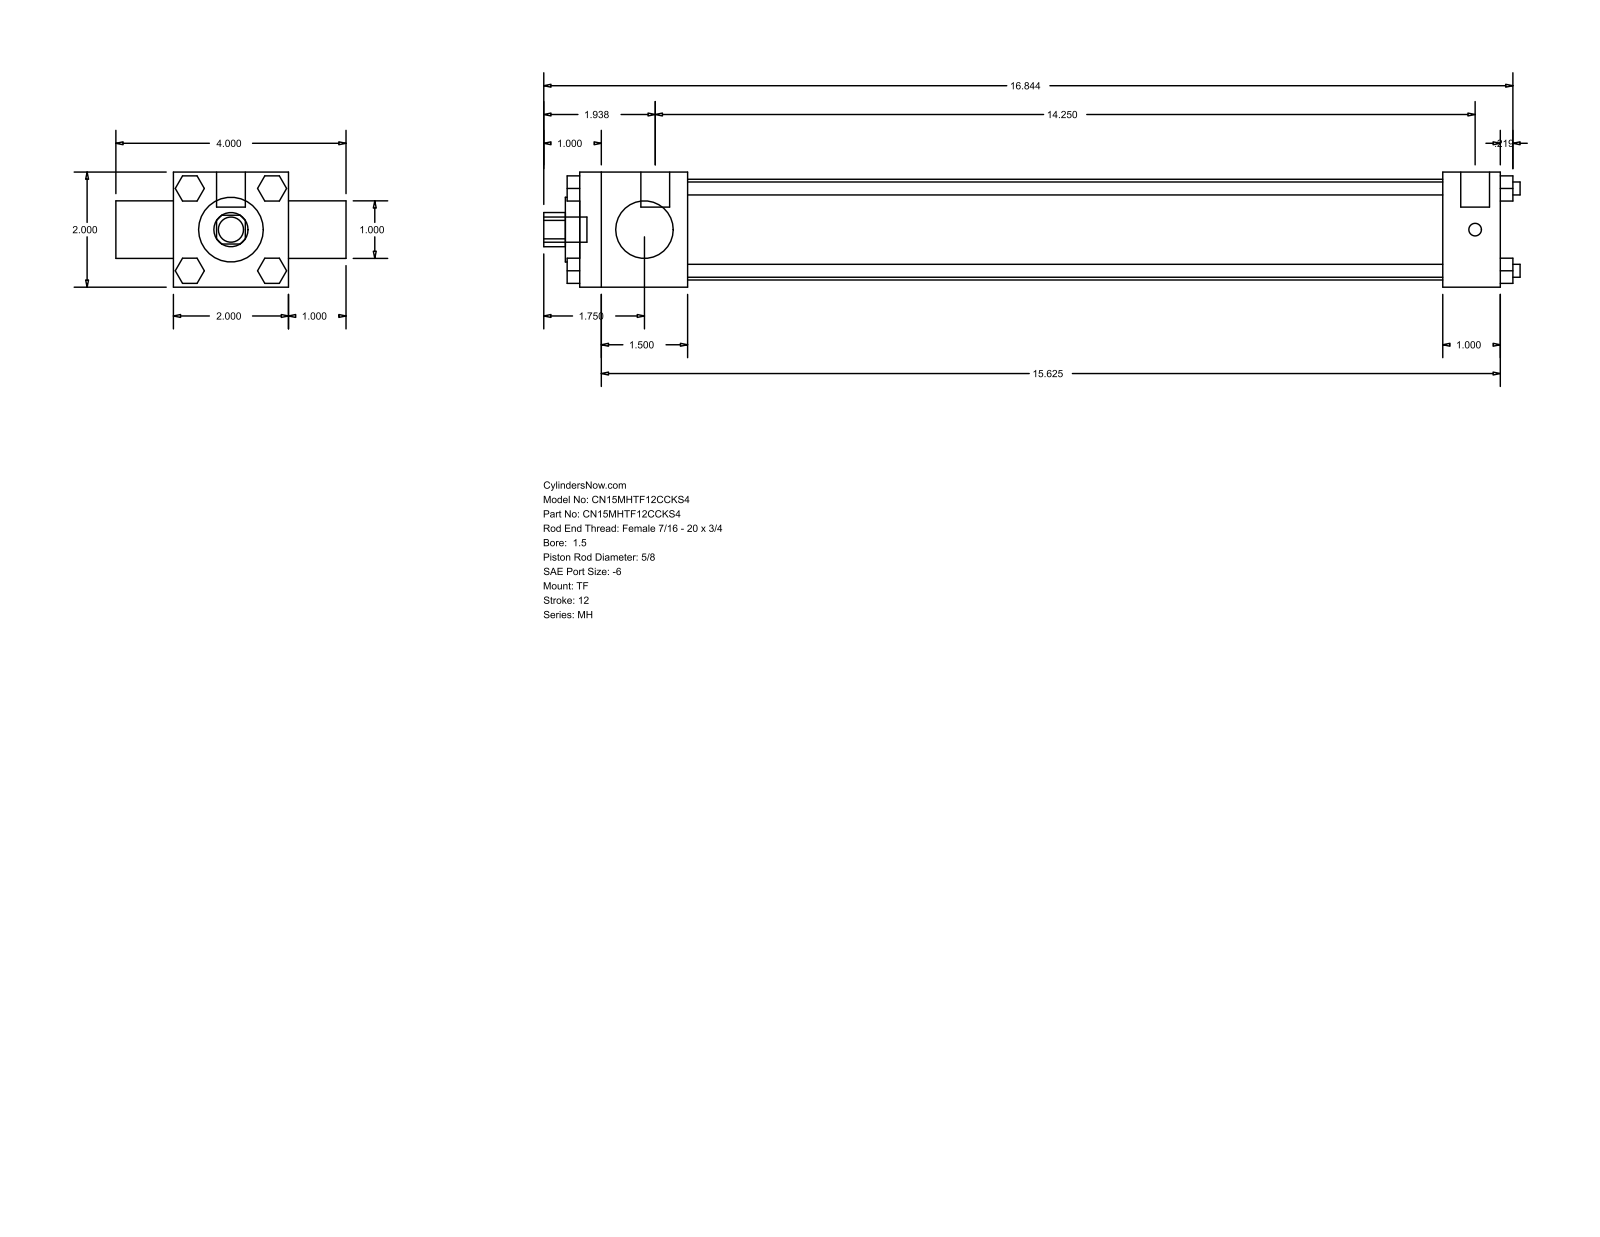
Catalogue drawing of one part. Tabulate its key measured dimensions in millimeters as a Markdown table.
| quantity | value |
| --- | --- |
| part name | MH_TF__0150_0.625 |
| STEP written by | GSSL Pune (CONFIG_CONTROL_DESIGN) |
| units | millimeters |
| bodies | 0 solids, 120 faces (92 planar, 28 cylindrical, 0 other) |
| overall size | 431.01 × 101.6 × 50.8 |
| round holes (diameter × count) | 15.88 × 1, 25.4 × 1, 28.57 × 1, 44.45 × 1 |
| round bosses / shafts (diameter × count) | 5.71 × 4, 5.56 × 3, 12.7 × 2, 11.11 × 1 |
| partial cylindrical surfaces (radius × count) | 7.54 × 1 |
| main face-to-face distances | 50.8, 406.39, 25.4, 76.2, 47.62, 358.77, 381, 333.38, 25.39, 5.56 |
